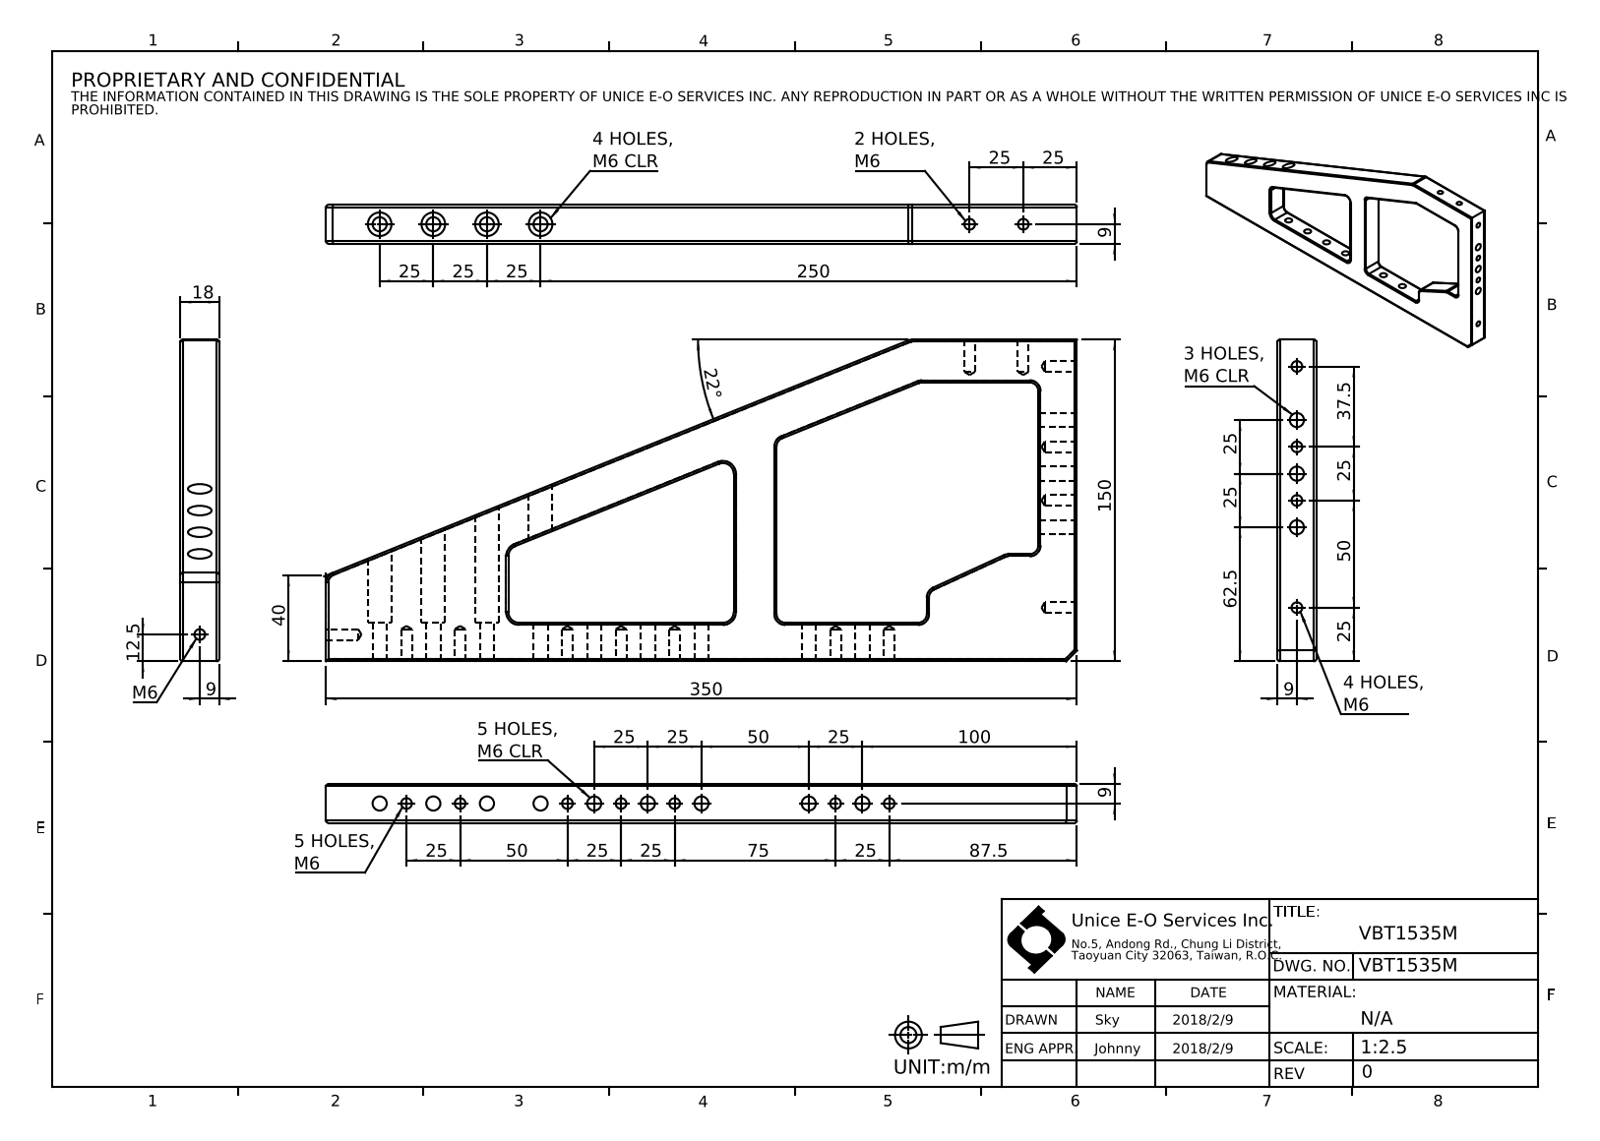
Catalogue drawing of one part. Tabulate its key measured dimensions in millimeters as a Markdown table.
| quantity | value |
| --- | --- |
| part name | U-F1-VBT1535-1M-DP; VBT1535M |
| STEP written by | SolidWorks 2016 (AUTOMOTIVE_DESIGN) |
| units | millimeters |
| bodies | 1 solid, 190 faces (23 planar, 111 cylindrical, 56 other) |
| overall size | 350 × 150 × 18 |
| volume | 338 925 mm³ |
| surface area | 80 819 mm² |
| round holes (diameter × count) | 5 × 14, 6.6 × 12, 11 × 4 |
| partial cylindrical surfaces (radius × count) | 1 × 33, 5 × 8, 4 × 6 |
| main face-to-face distances | 18, 20, 20.41, 140, 132, 150, 20.45, 122, 160, 142 |
| hole center spacings | 12.5, 25, 37.5, 75, 50, 62.5, 87.5, 100 |
